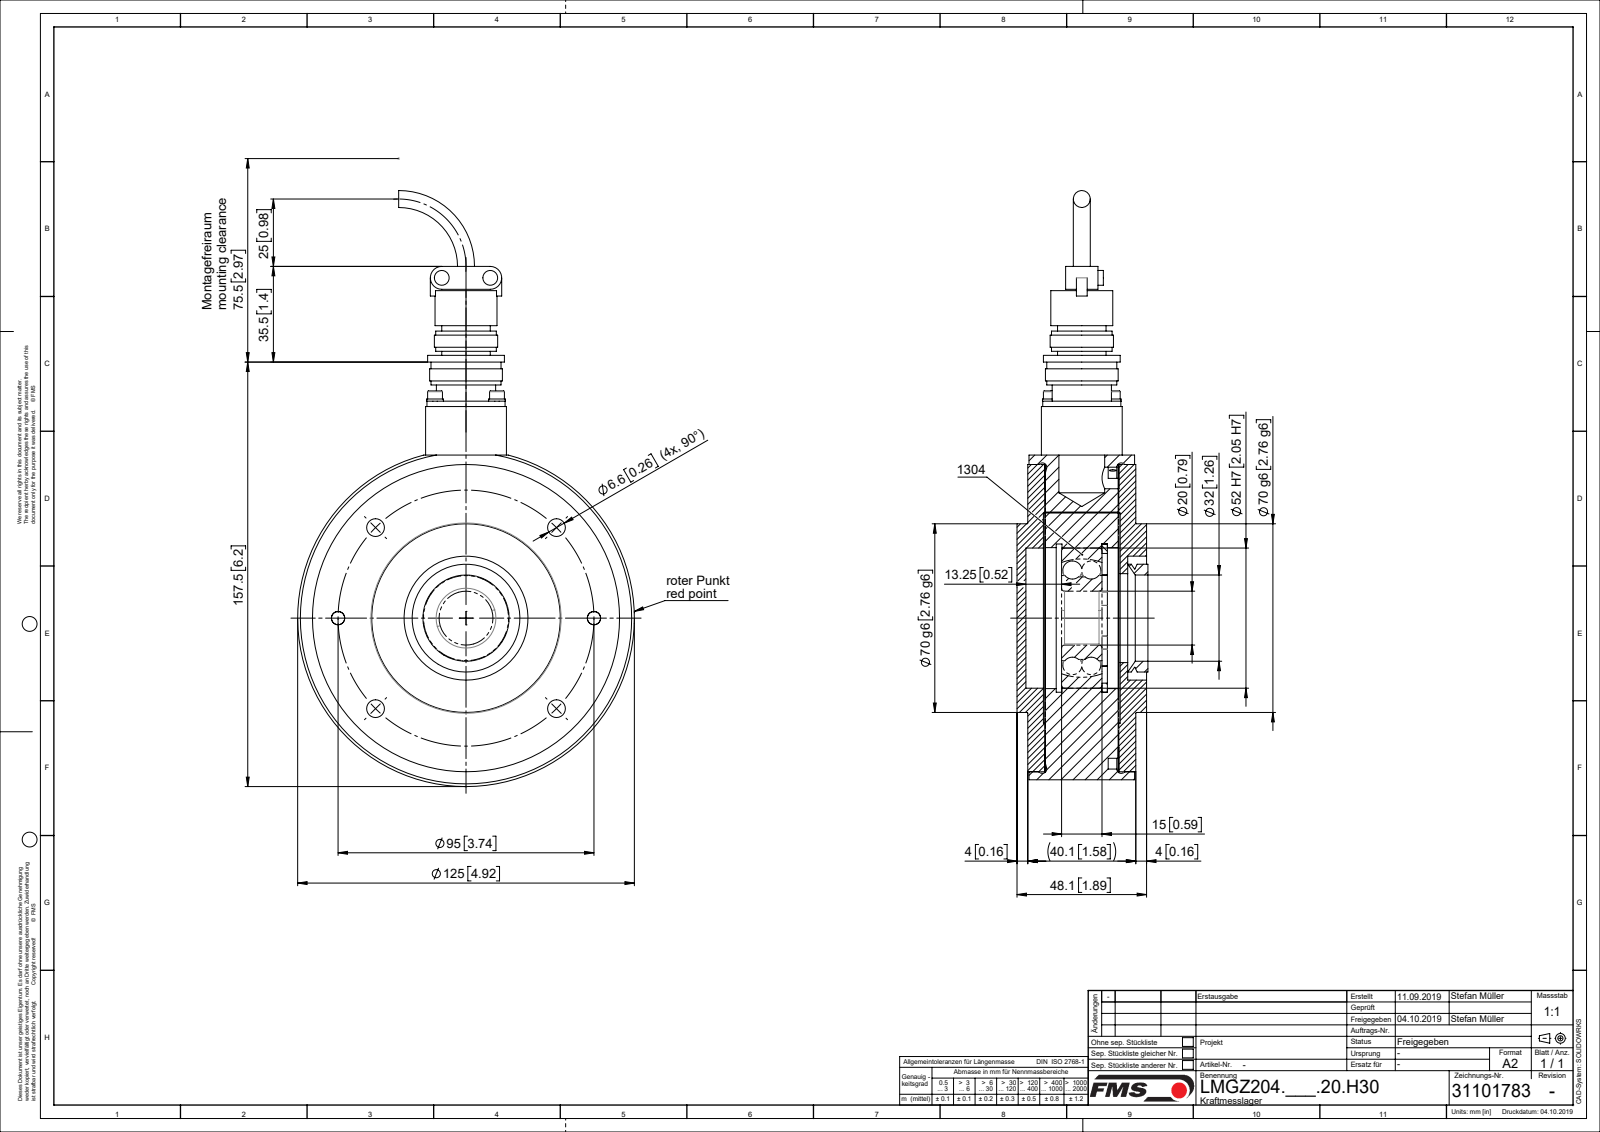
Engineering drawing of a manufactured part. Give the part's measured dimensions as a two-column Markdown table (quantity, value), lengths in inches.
| quantity | value |
| --- | --- |
| part name | ZEICHNUNG7; L50059; L4832404; L47956 (+8 more) |
| STEP written by | Mechanical Desktop 2007 (CONFIG_CONTROL_DESIGN) |
| units | inches |
| bodies | 20 solids, 406 faces (110 planar, 244 cylindrical, 52 other) |
| overall size | 8.707 × 4.921 × 1.894 |
| volume | 29.55 in³ |
| surface area | 224.1 in² |
| round holes (diameter × count) | 0.26 × 6, 0.102 × 4, 0.126 × 4, 0.134 × 4, 0.197 × 2, 0.433 × 2, 0.787 × 1, 0.906 × 1, 1.22 × 1, 1.299 × 1, 1.492 × 1, 1.811 × 1 |
| round bosses / shafts (diameter × count) | 0.217 × 6, 0.244 × 4, 0.118 × 4, 0.098 × 4, 0.394 × 2, 0.236 × 2, 4.921 × 1, 4.488 × 1 |
| partial cylindrical surfaces (radius × count) | 0.197 × 8, 0.167 × 2, 1.594 × 1, 1.85 × 1 |
| main face-to-face distances | 1.073, 1.321, 0.248, 0.258, 1.331, 1.063, 1.083, 0.157, 0.415, 1.488 |
| hole center spacings | 1.87, 0.64, 0.906, 1.431, 2.645, 3.456, 1.281, 3.741 |
